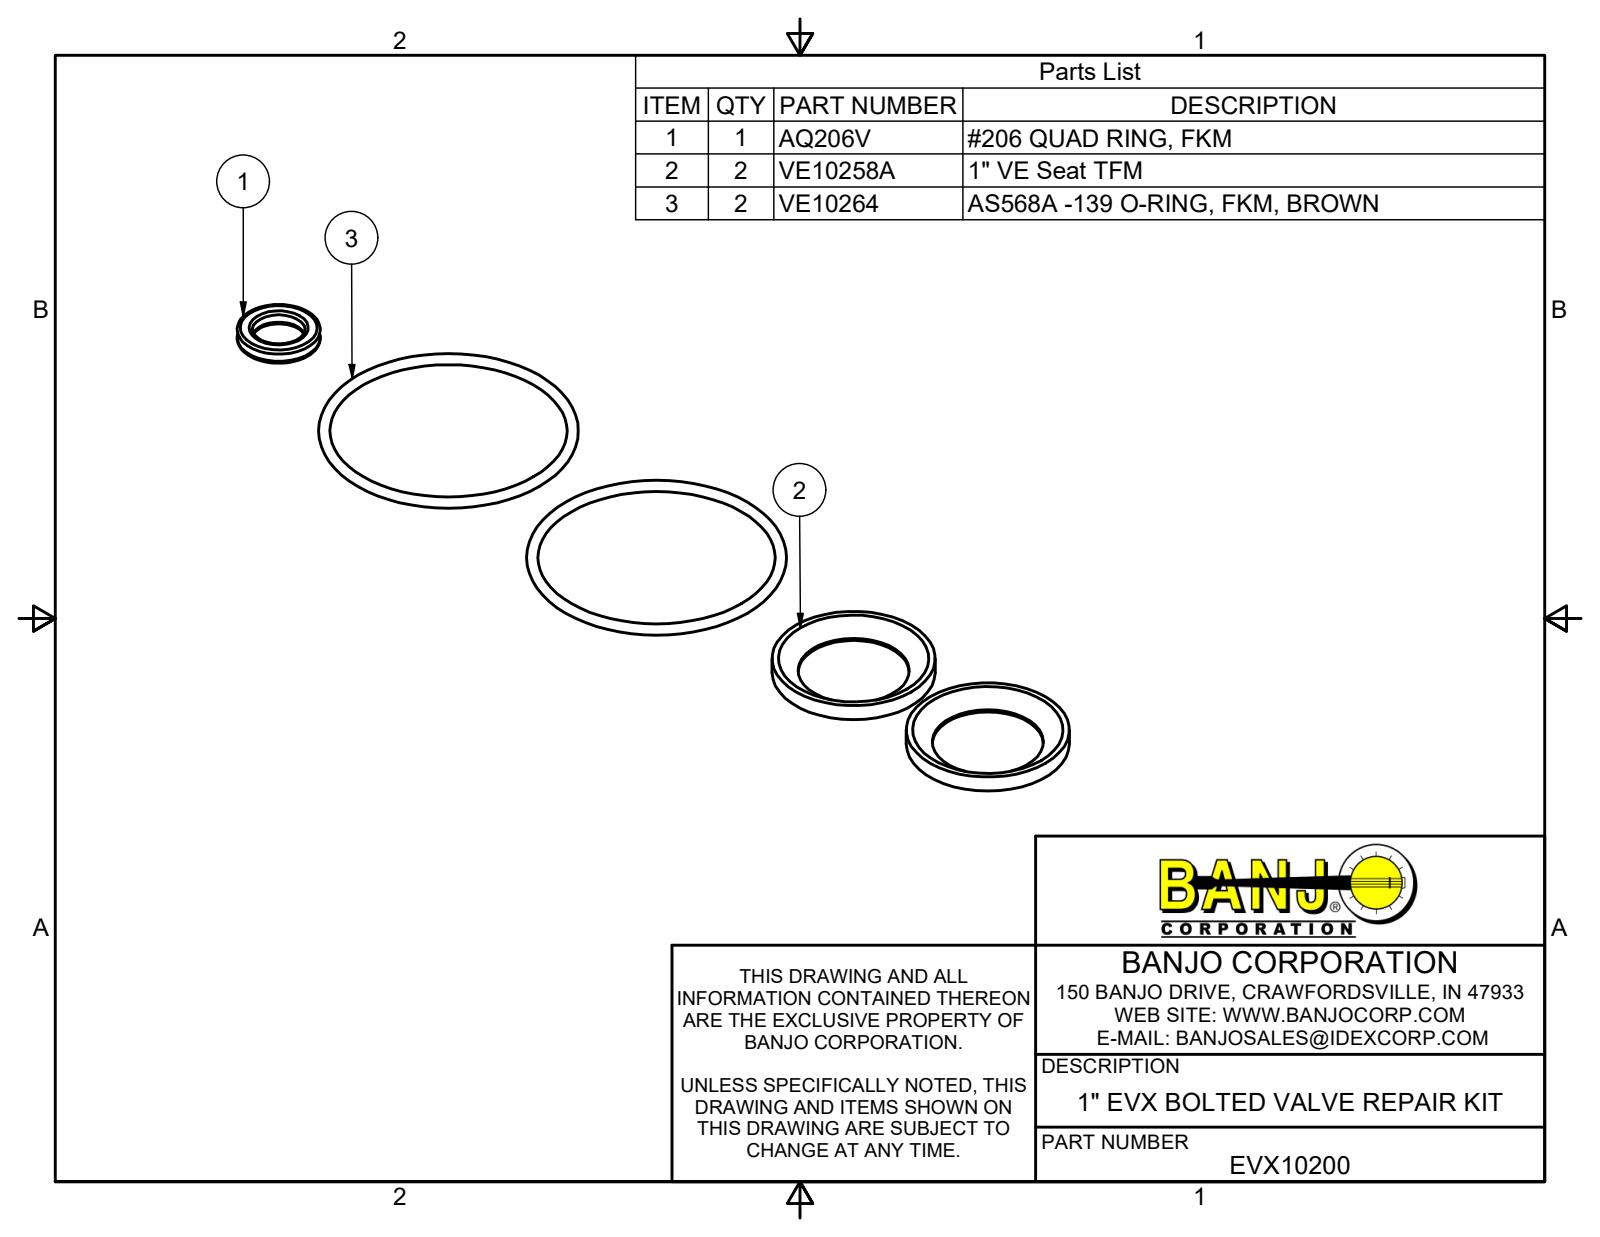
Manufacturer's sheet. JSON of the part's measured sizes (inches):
{"part_name": "EVX10200; AQ206V; VE10264; VE10258A", "step_written_by": "Autodesk Inventor 2022 (AUTOMOTIVE_DESIGN)", "units": "inches", "bodies": {"solids": 5, "faces": 32, "planar": 8, "cylindrical": 4, "other": 20}, "overall_size": [10.254, 2.456, 0.171], "volume_in3": 0.364, "surface_area_in2": 11.46, "round_holes": [[1.02, 2]], "round_bosses_or_shafts": [[1.495, 2]], "face_to_face_distances": [0.158, 0.013, 0.171], "hole_center_spacings": [1.672]}
